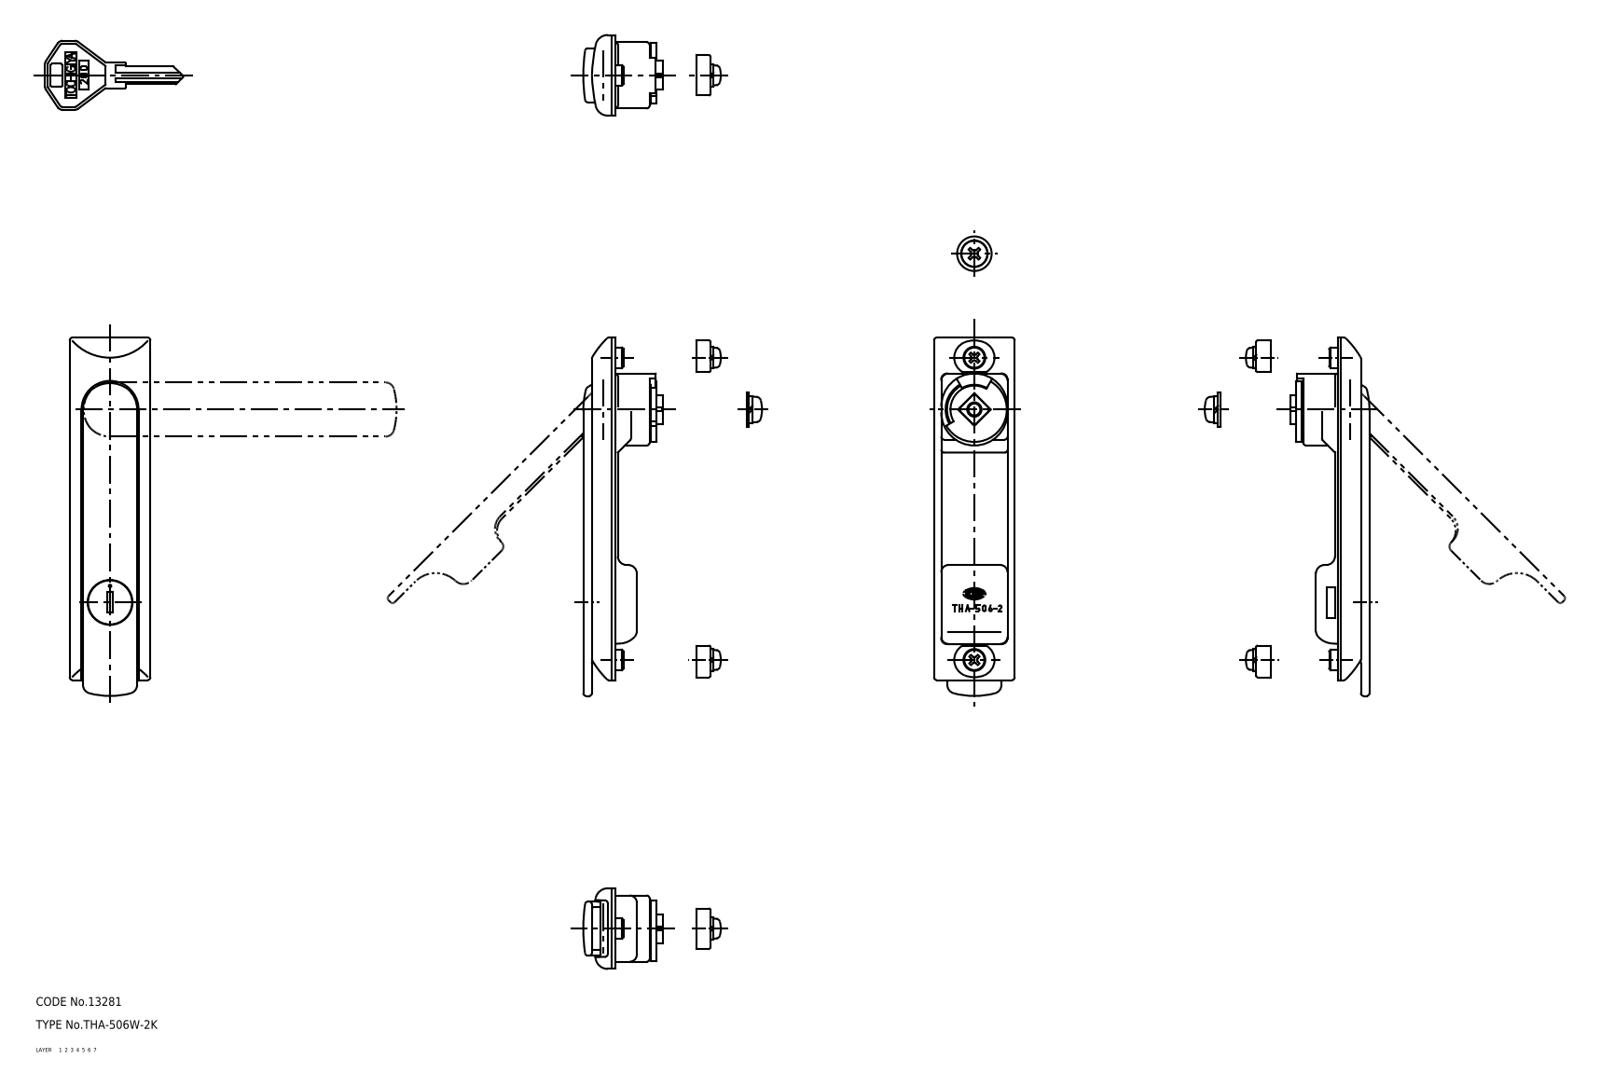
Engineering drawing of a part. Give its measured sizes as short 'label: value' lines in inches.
name: THA_506W_2K
written by: SolidWorks 2003240 (AUTOMOTIVE_DESIGN)
unit: in
bodies: 13 solids, 482 faces (184 planar, 194 cylindrical, 104 other)
size: 4.902 × 3.554 × 1.102
volume: 2.15 in³; area: 46.9 in²
holes: 3× ⌀0.157, 2× ⌀0.165, 2× ⌀0.276, 2× ⌀0.299, 1× ⌀0.197, 1× ⌀0.469, 1× ⌀0.614, 1× ⌀0.63, 1× ⌀0.783
bosses: 1× ⌀0.787, 1× ⌀0.744, 1× ⌀0.602, 1× ⌀0.547, 1× ⌀0.472, 1× ⌀0.465, 1× ⌀0.362
rounds: 32× R0.039, 12× R0.079, 7× R0.02, 7× R0.118, 6× R0.059, 5× R0.157, 4× R0.012, 4× R0.098
face distances: 0.079, 0.039, 0.26, 0.181, 0.161, 0.02, 0.76, 0.333, 0.098, 0.354
hole spacings: 0.709, 0.787, 2.638, 3.346, 3.425, 4.134
